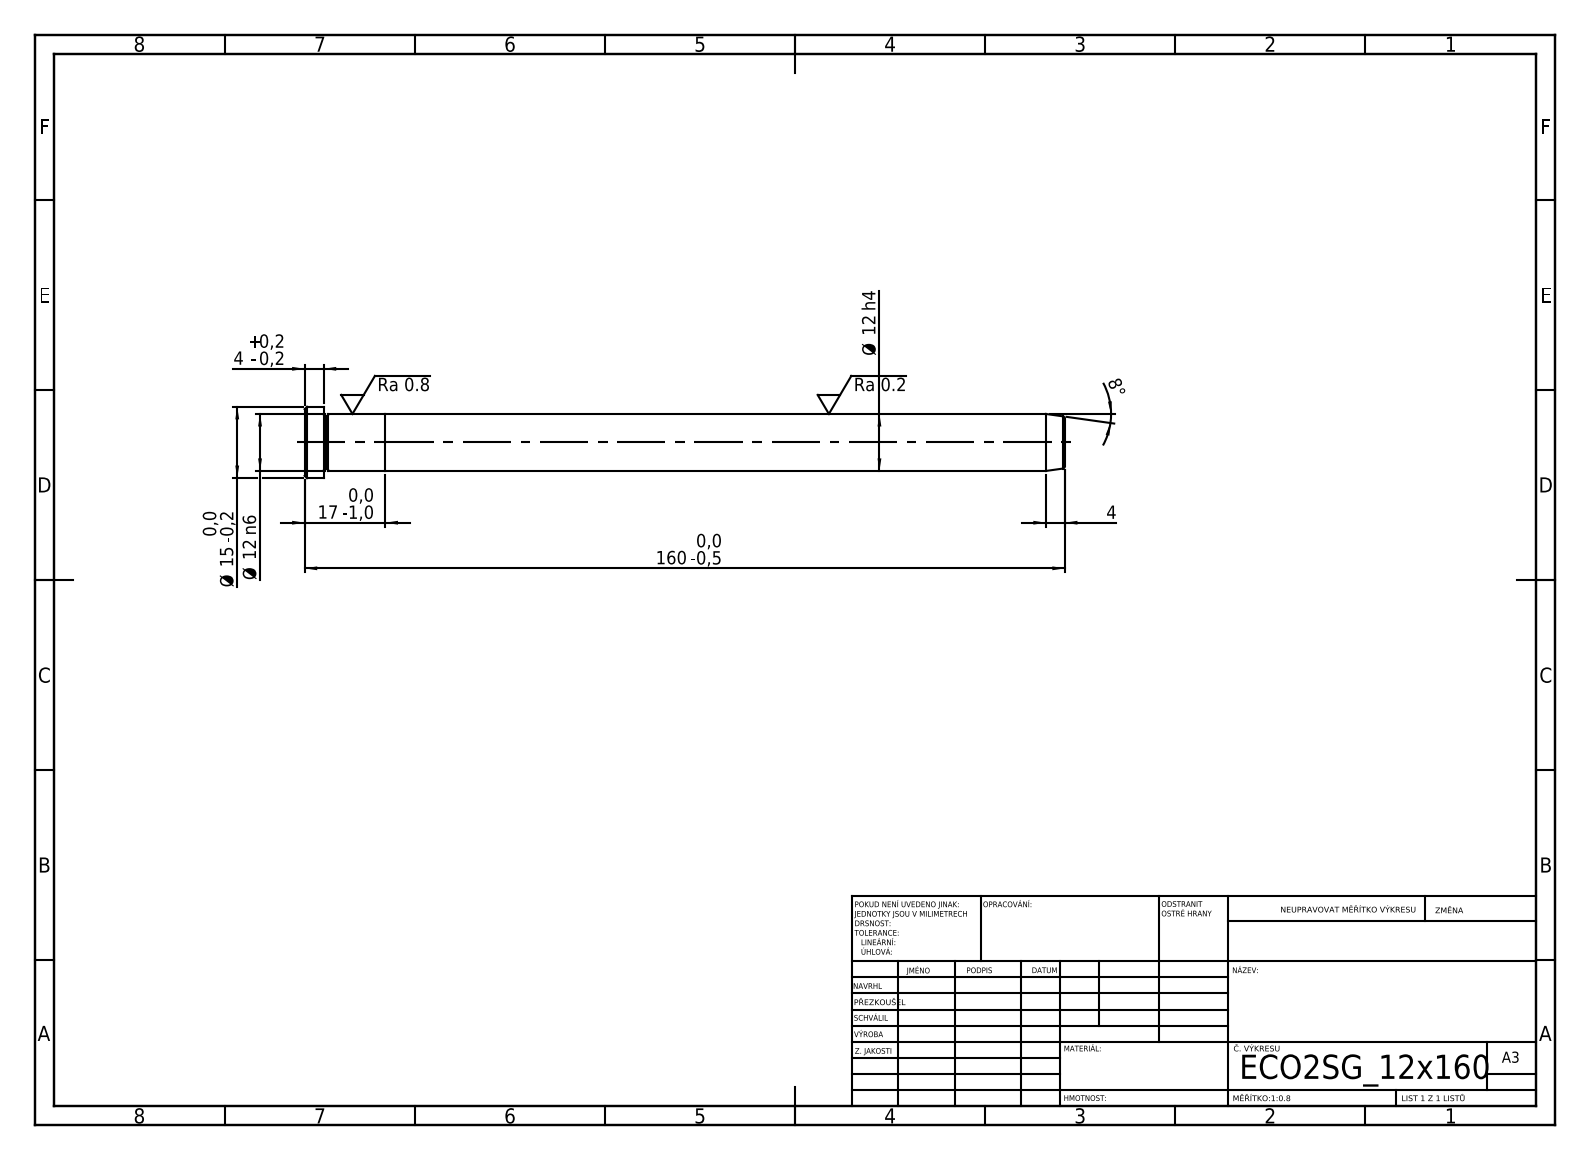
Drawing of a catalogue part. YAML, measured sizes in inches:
step_written_by: "SolidWorks 2019 (CONFIG_CONTROL_DESIGN)"
units: inches
bodies: {solids: 2, faces: 21, planar: 5, cylindrical: 6, other: 10}
overall_size: [6.299, 0.591, 0.591]
volume: 1.116
surface_area: 10.26
round_bosses_or_shafts:
  - {diameter: 0.591, count: 1}
  - {diameter: 0.472, count: 1}
face_to_face_distances: [0.669, 5.63, 6.299, 6.142, 0.512, 0.157]
